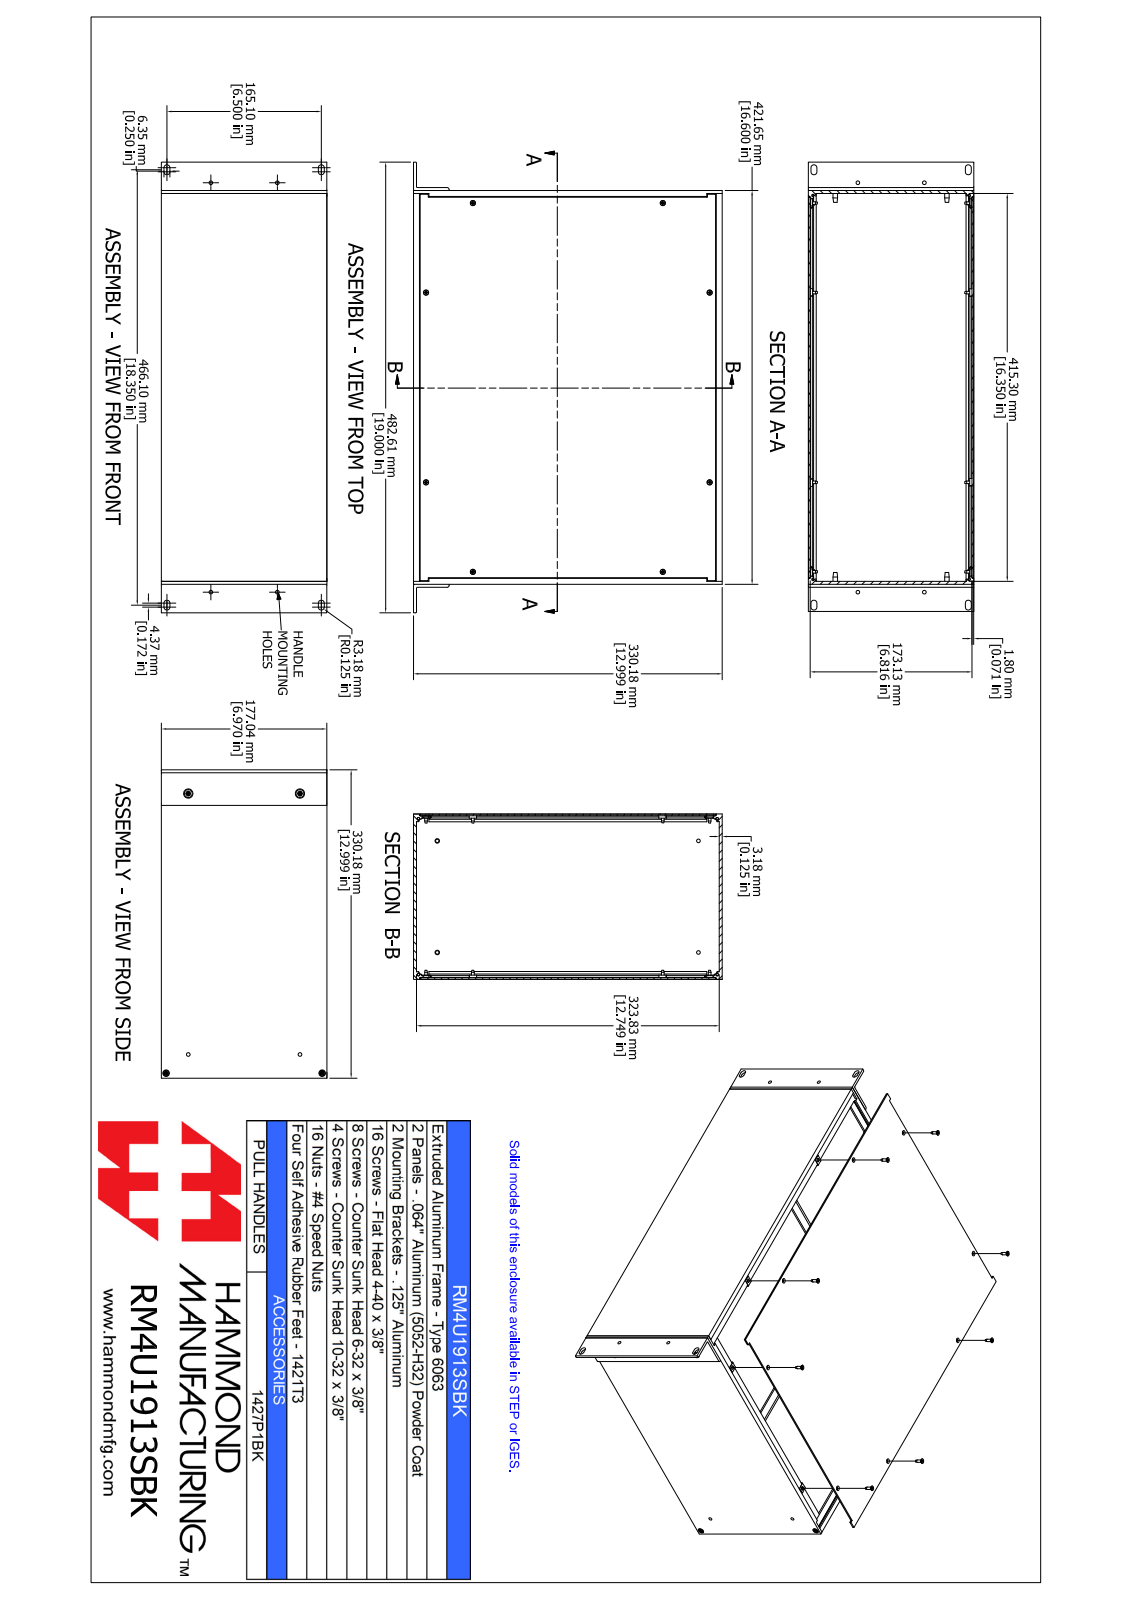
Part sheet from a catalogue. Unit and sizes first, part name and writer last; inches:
Units: inches
Overall size (bounding box): 19 × 12.999 × 6.971
Round holes (diameter × count): ⌀0.118 ×9, ⌀0.098 ×8, ⌀0.157 ×8, ⌀0.138 ×4, ⌀0.156 ×4, ⌀0.157 ×4, ⌀0.165 ×4, ⌀0.169 ×4, ⌀0.197 ×2
Round bosses / shafts (diameter × count): ⌀0.214 ×12, ⌀0.112 ×12, ⌀0.238 ×4, ⌀0.138 ×4, ⌀0.333 ×2, ⌀0.19 ×2
Partial cylindrical surfaces — rounded edges, fillets, slot ends (radius × count): R0.039 ×22, R0.015 ×16, R0.038 ×16, R0.049 ×16, R0.055 ×8, R0.125 ×8, R0.131 ×8, R0.079 ×2
Main face-to-face distances: 0.071, 6.887, 0.125, 6.816, 6.958, 16.475, 0.125, 12.874, 12.999, 12.749
Hole centre spacings: 8, 11.937, 15.428, 4.257, 10.662, 10.662, 11.826, 1.224
Volume: 91.41 in³ · Surface area: 1 878 in²
Bodies: 52 solids, 1372 faces (636 planar, 240 cylindrical, 496 other)
Part name (STEP PRODUCT): RM4U1913SBK
STEP written by: SolidWorks 2021 (AUTOMOTIVE_DESIGN)
